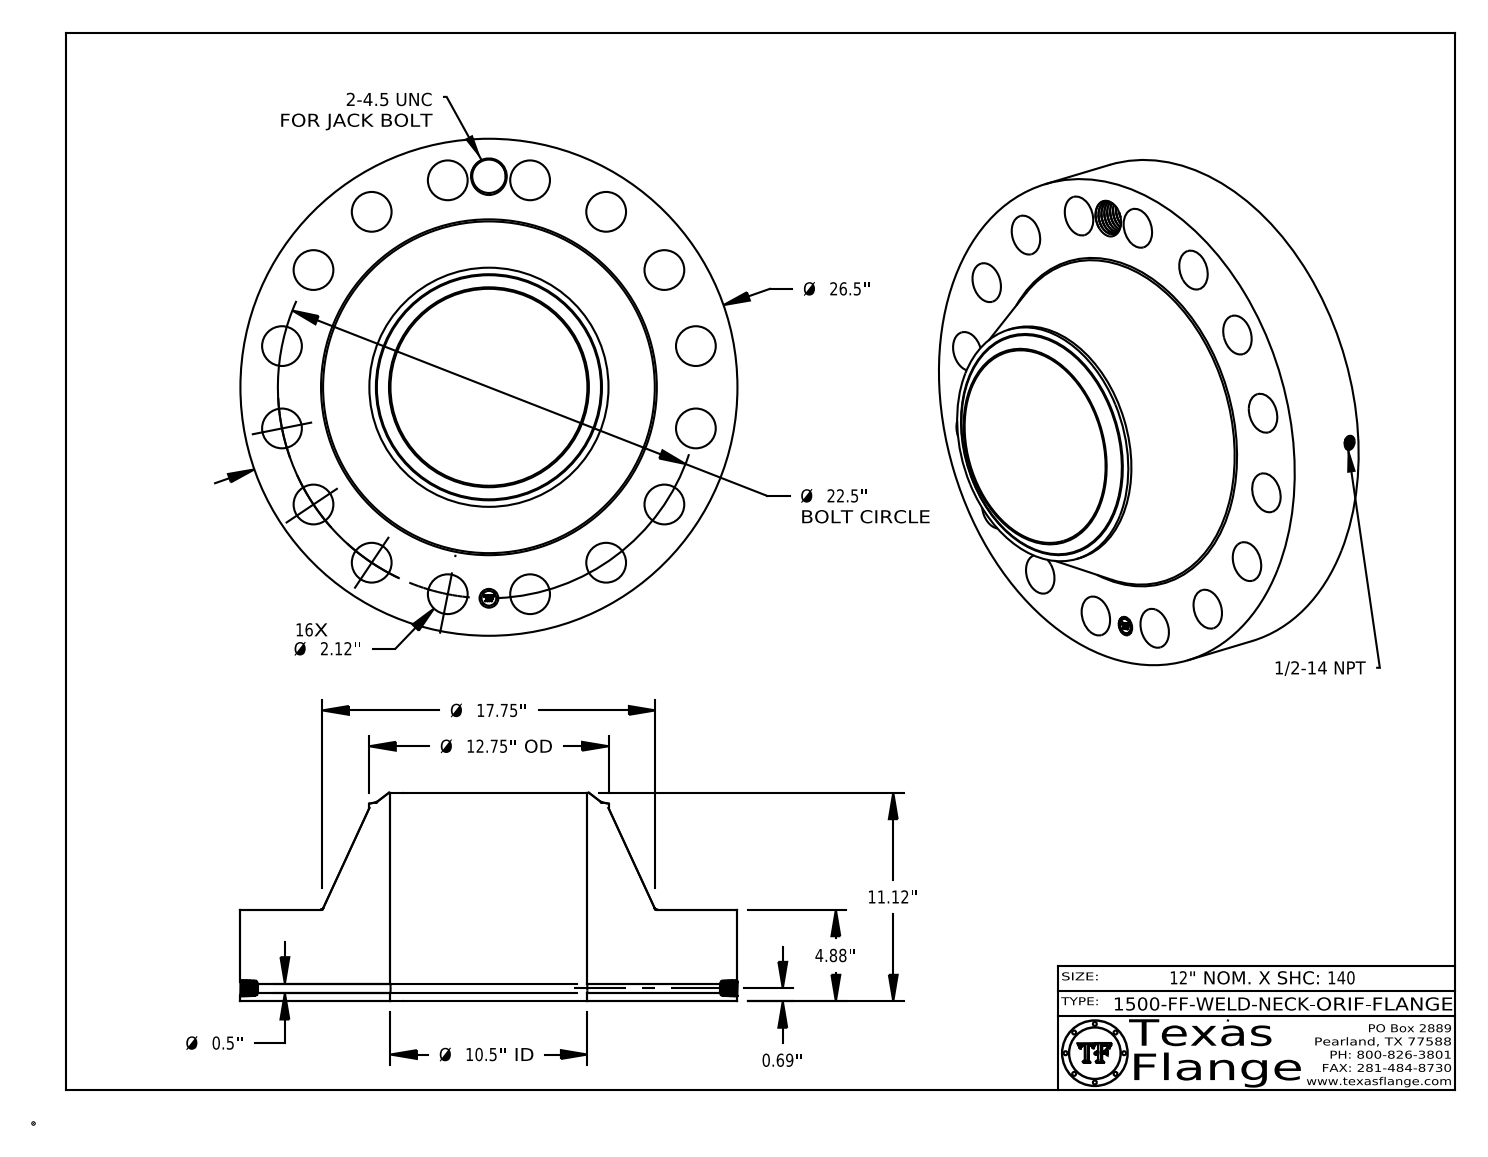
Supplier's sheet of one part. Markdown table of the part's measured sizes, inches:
| quantity | value |
| --- | --- |
| part name | 1500-FF-WELD-NECK |
| STEP written by | CATIA V5 STEP AP214 (AUTOMOTIVE_DESIGN) |
| units | inches |
| bodies | 1 solid, 828 faces (368 planar, 122 cylindrical, 338 other) |
| overall size | 26.5 × 26.5 × 11.12 |
| volume | 2 525 in³ |
| surface area | 2 355 in² |
| round holes (diameter × count) | 2.12 × 16, 0.5 × 1, 0.672 × 1, 1 × 1, 1.781 × 1, 10.5 × 1 |
| round bosses / shafts (diameter × count) | 0.061 × 8, 26.5 × 1, 12.75 × 1, 0.788 × 1 |
| main face-to-face distances | 4.88, 11.12, 6.24, 4.865, 0.015, 6.255, 0.298, 0.293, 0.054, 0.248 |
| hole center spacings | 11.25, 8.61, 15.91, 20.787, 12.5, 18.708, 22.068, 4.389 |
